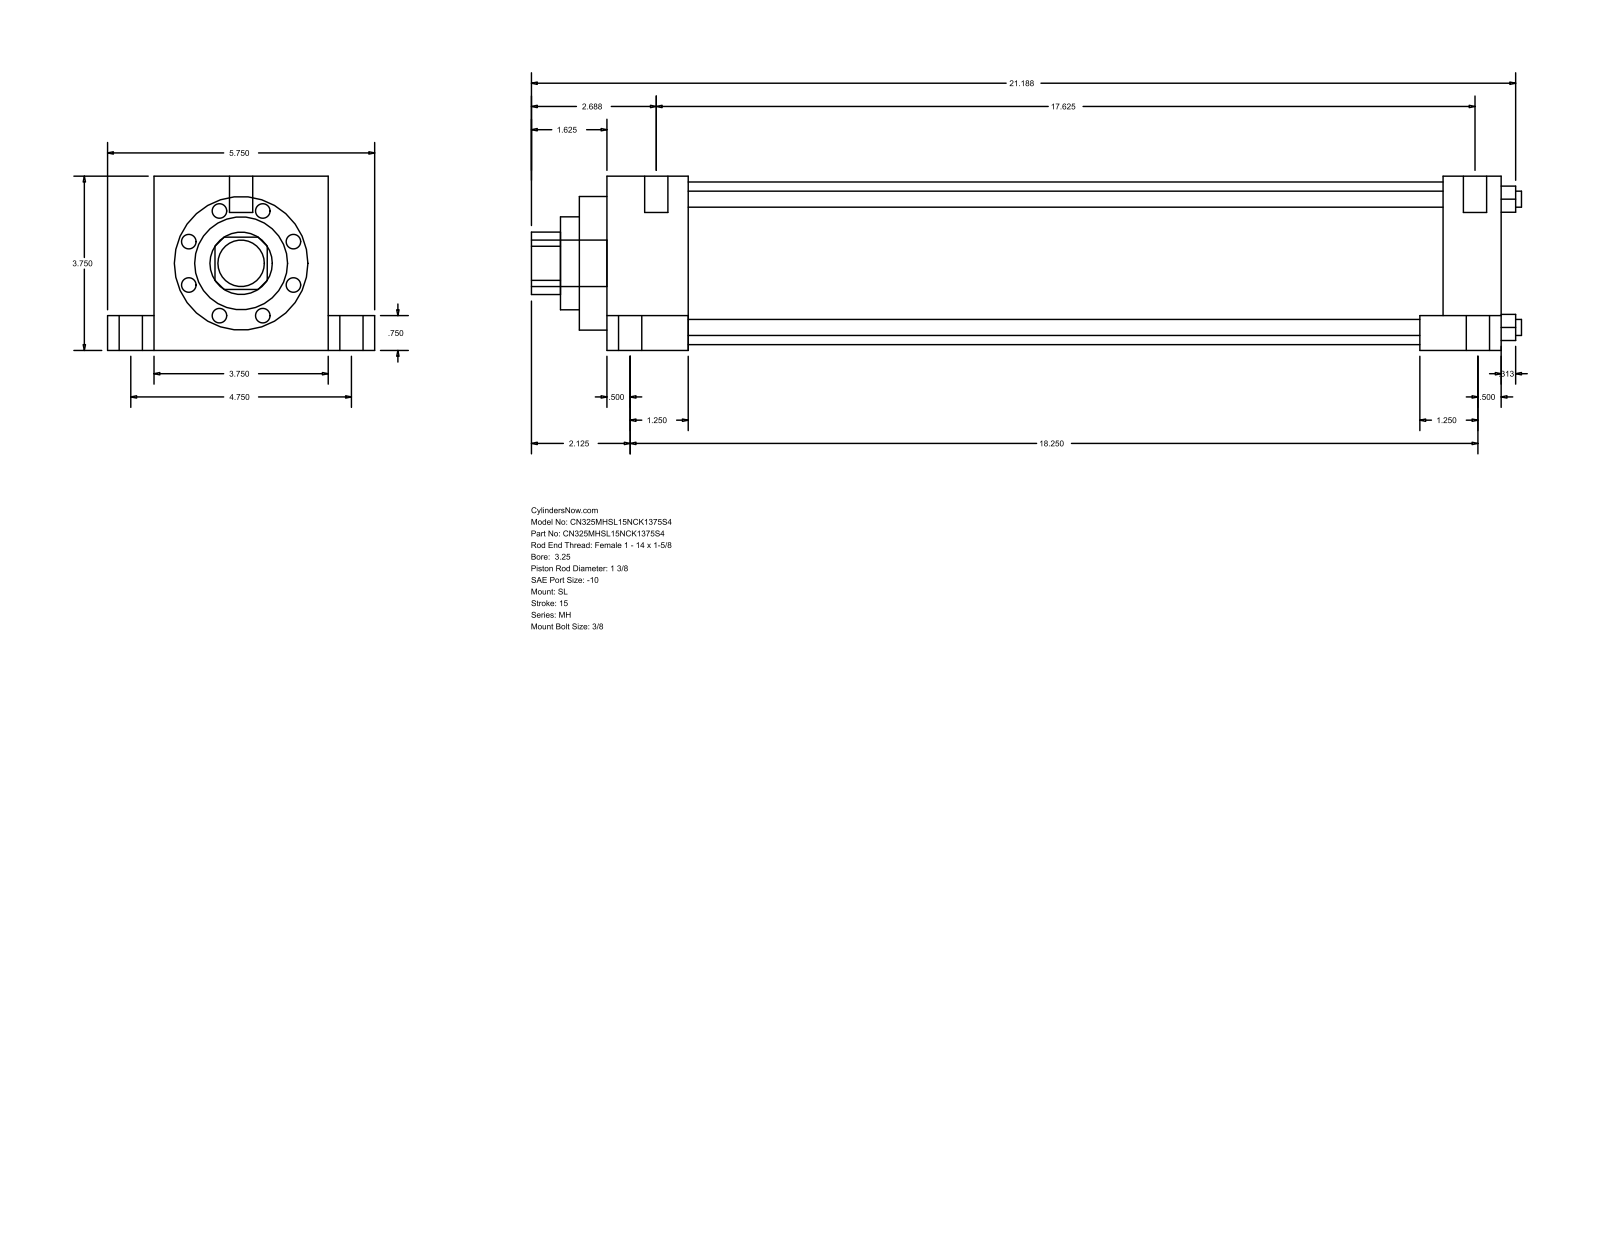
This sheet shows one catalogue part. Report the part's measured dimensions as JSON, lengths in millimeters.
{"part_name": "MH_SL__0325_1.375", "step_written_by": "GSSL Pune (CONFIG_CONTROL_DESIGN)", "units": "millimeters", "bodies": {"solids": 0, "faces": 110, "planar": 77, "cylindrical": 33, "other": 0}, "overall_size": [541.34, 146.05, 95.25], "round_holes": [[8.76, 4], [34.92, 1], [50.8, 1], [73.03, 1], [88.9, 1]], "round_bosses_or_shafts": [[12.7, 6], [19.05, 4], [5.56, 4], [25.4, 1]], "partial_cylinders_radius": [[17.06, 1]], "face_to_face_distances": [95.24, 488.96, 44.45, 444.51, 25.41, 120.65, 19.05, 76.19, 457.21, 412.76], "hole_center_spacings": [49.57, 70.1, 99.14]}
